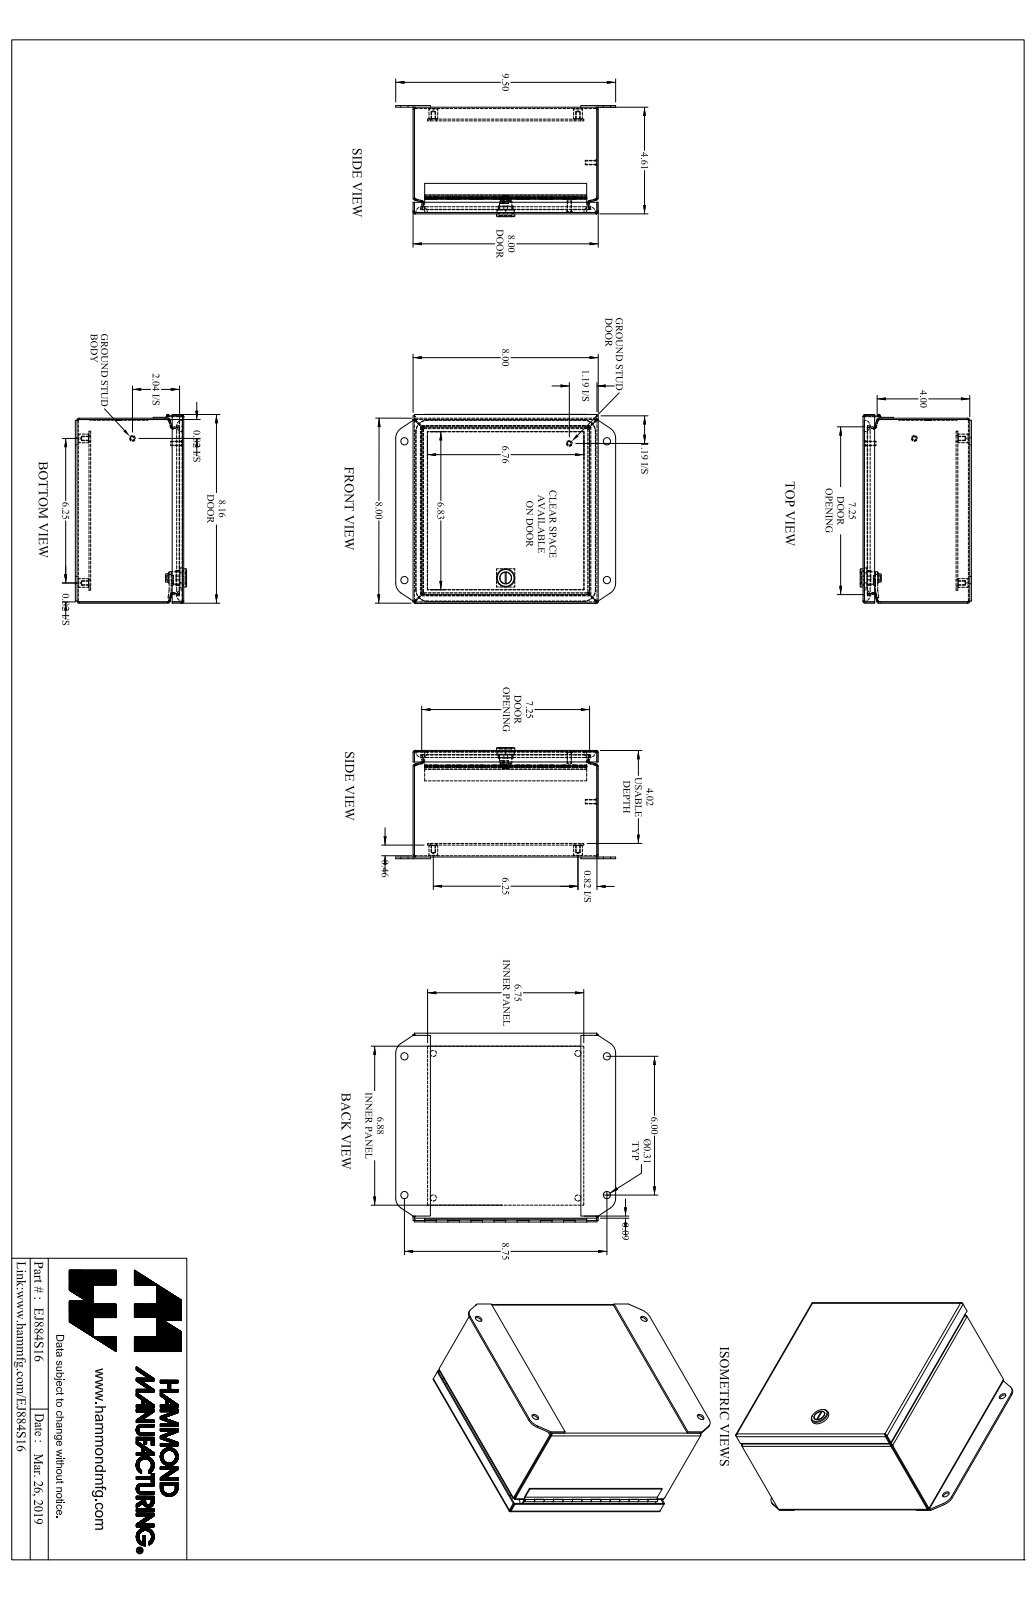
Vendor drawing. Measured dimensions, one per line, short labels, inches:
name: EJ884S16_Default
written by: SolidWorks 2019 (CONFIG_CONTROL_DESIGN)
unit: in
bodies: 16 solids, 564 faces (294 planar, 190 cylindrical, 80 other)
size: 9.5 × 8.165 × 4.805
volume: 24.9 in³; area: 817.6 in²
holes: 4× ⌀0.156, 4× ⌀0.265, 4× ⌀0.313, 1× ⌀0.05, 1× ⌀0.516
bosses: 4× ⌀0.375, 2× ⌀0.25, 2× ⌀0.19, 1× ⌀0.788, 1× ⌀0.535, 1× ⌀0.496, 1× ⌀0.435, 1× ⌀0.1
rounds: 16× R0.029, 16× R0.086, 12× R0.281, 4× R0.25, 4× R0.499, 4× R0.5, 2× R0.06, 1× R0.03
face distances: 0.057, 4.554, 7.943, 0.072, 0.589, 7.886, 8, 4.611, 4.497, 4.094
hole spacings: 6.25, 3.133, 1.256, 1.256, 6.251, 7.501, 7.502, 9.683
